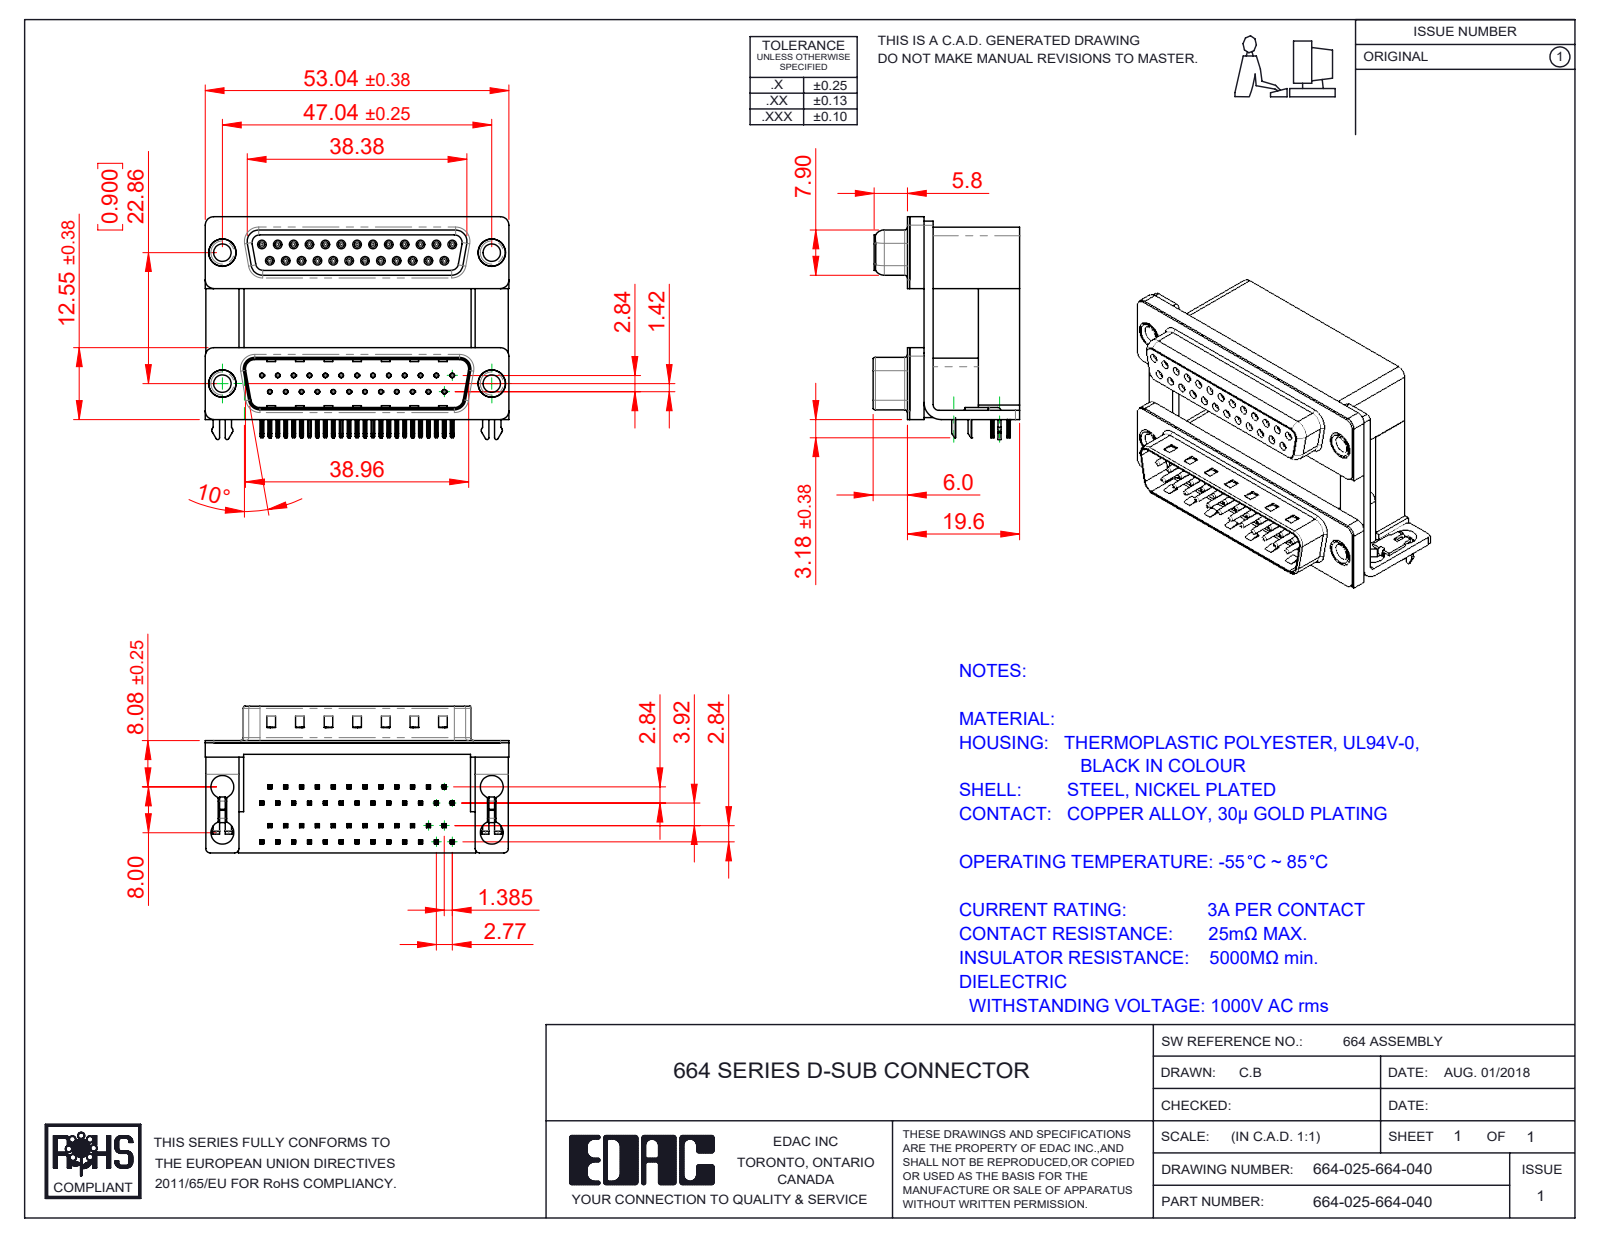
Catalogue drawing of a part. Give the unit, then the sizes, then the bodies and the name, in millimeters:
Units: millimetres
Overall size (bounding box): 53.04 × 38.91 × 25.6
Round holes (diameter × count): ⌀0.8 ×50, ⌀0.35 ×25, ⌀0.9 ×25, ⌀4 ×8, ⌀3.05 ×4, ⌀3.5 ×4, ⌀4.8 ×4, ⌀5 ×4
Round bosses / shafts (diameter × count): ⌀1.2 ×25, ⌀0.75 ×25, ⌀4.9 ×4, ⌀4.75 ×4, ⌀3.85 ×4
Partial cylindrical surfaces — rounded edges, fillets, slot ends (radius × count): R0.1 ×201, R0.25 ×106, R0.15 ×100, R0.12 ×50, R0.35 ×50, R0.34 ×25, R0.5 ×16, R1.5 ×14
Main face-to-face distances: 19.2, 12, 0.4, 7.2, 10.7, 2.84, 16.7, 9.5, 2.5, 12.4
Hole centre spacings: 2.77, 3.16, 5.54, 8.31, 11.08, 13.85, 16.62, 5.03
Volume: 23 594 mm³ · Surface area: 25 215 mm²
Bodies: 63 solids, 6227 faces (3335 planar, 1537 cylindrical, 1355 other)
Part name (STEP PRODUCT): 664 Contact Top Lower; 664 Shell Receptacle_25 Contacts; 664 Contact Top Upper_H; 664 Contact Bottom Upper_H (+8 more)
STEP written by: SolidWorks 2020 (CONFIG_CONTROL_DESIGN)
